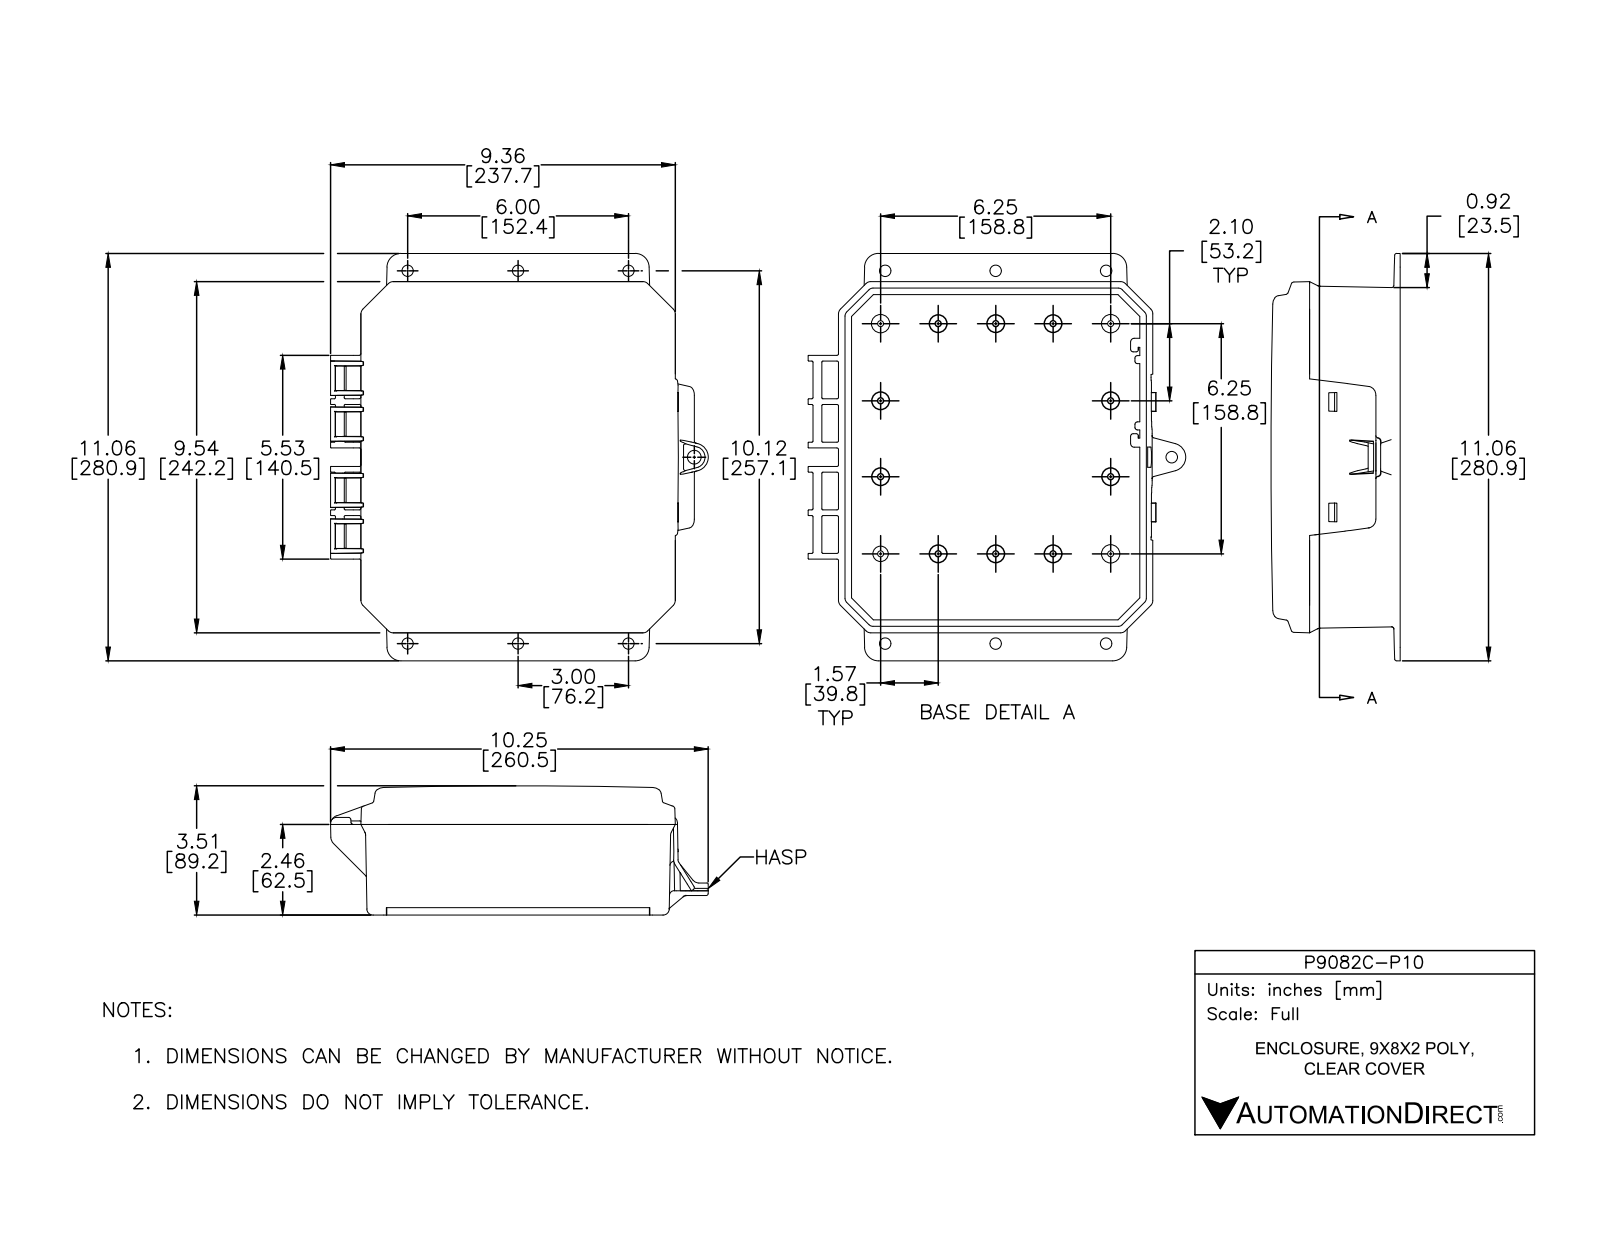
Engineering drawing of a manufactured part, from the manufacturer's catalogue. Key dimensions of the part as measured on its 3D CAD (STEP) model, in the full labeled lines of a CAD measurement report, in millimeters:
Part name (STEP PRODUCT): P98CHO; P982BH; P9082C
STEP written by: SolidWorks 2016 (AUTOMOTIVE_DESIGN)
Units: millimetres
Bodies: 2 solids, 1756 faces (407 planar, 674 cylindrical, 675 other)
Overall size (bounding box): 280.9 × 260.5 × 89.2
Volume: 755 600 mm³ · Surface area: 411 600 mm²
Round holes (diameter × count): ⌀4.1 ×14
Round bosses / shafts (diameter × count): ⌀6.1 ×1
Partial cylindrical surfaces — rounded edges, fillets, slot ends (radius × count): R0.5 ×84, R1 ×72, R0.8 ×64, R0.4 ×60, R1.5 ×40, R0.3 ×37, R1.3 ×24, R4.8 ×17
Main face-to-face distances: 3.8, 12, 9.5, 62.5, 58.7, 2.5, 3, 195.9, 207.9, 233.3
Hole centre spacings: 158.8, 39.6, 39.8, 53.2, 66.4, 79.4, 95.6, 105.5
